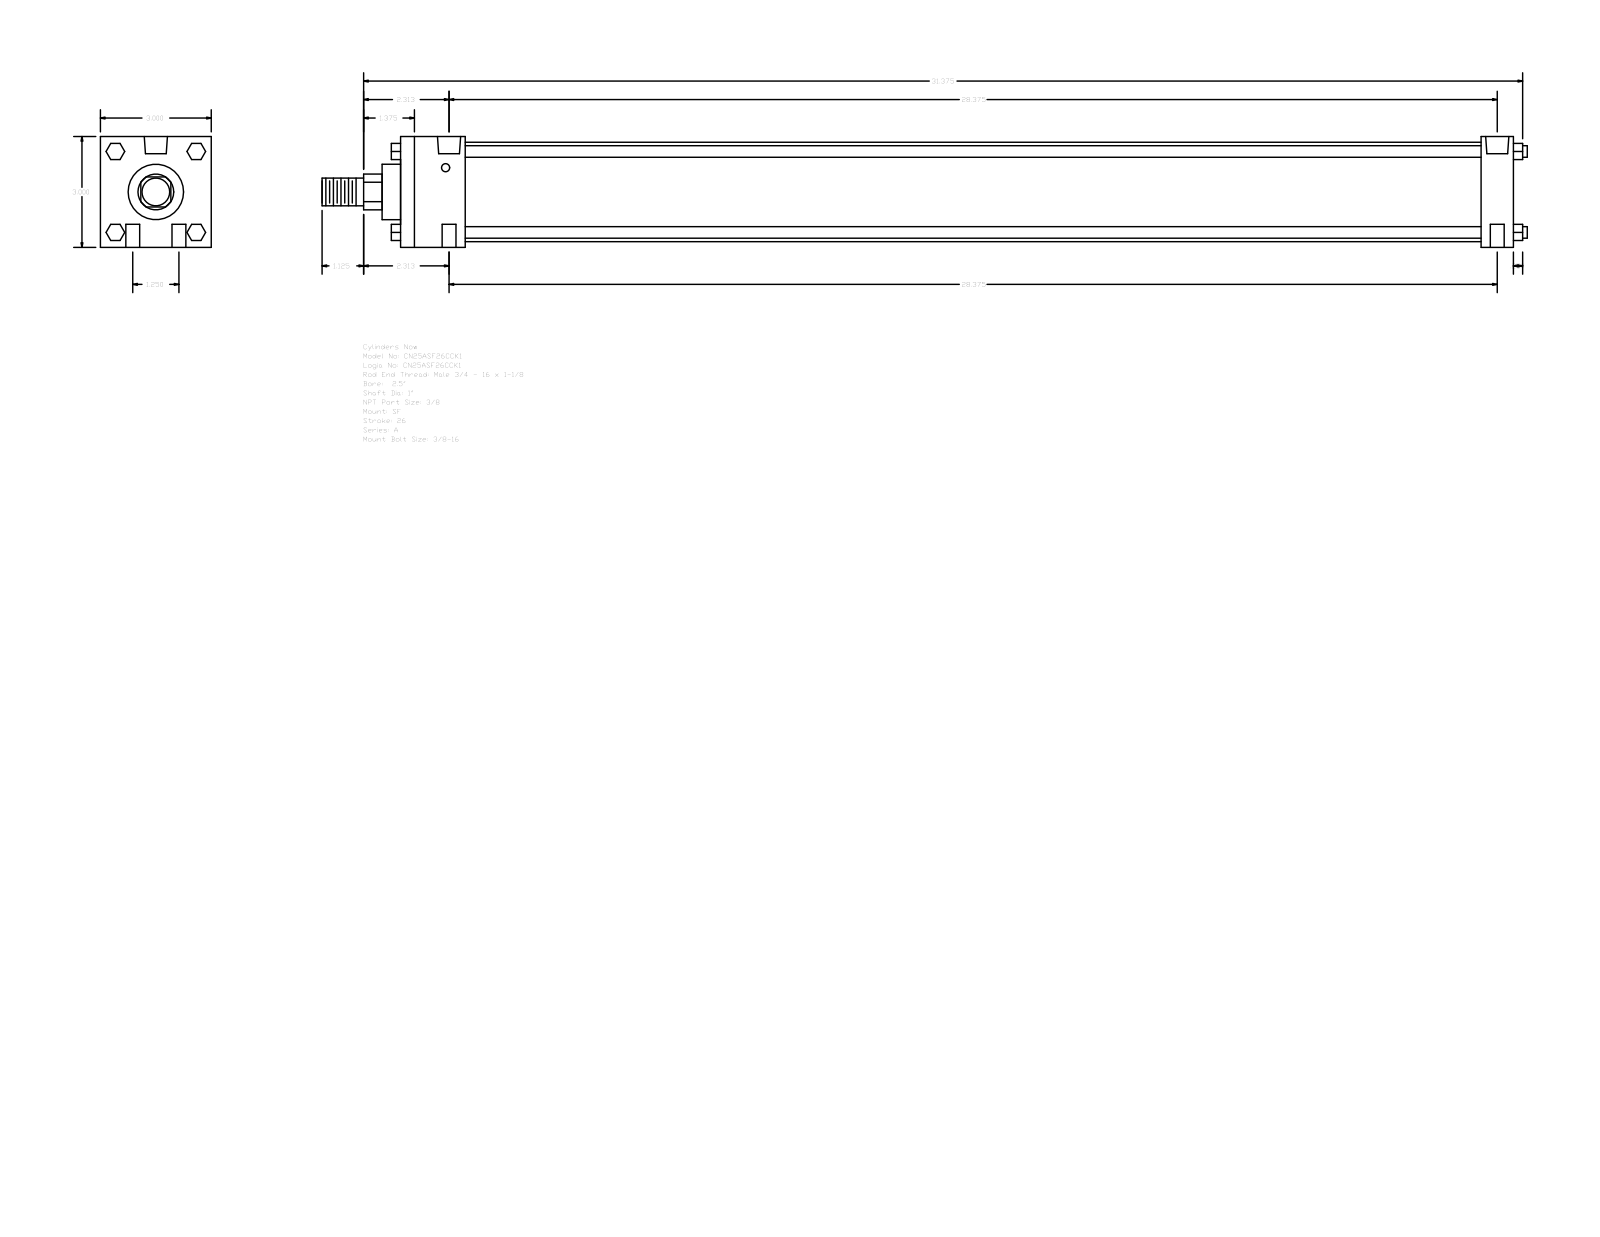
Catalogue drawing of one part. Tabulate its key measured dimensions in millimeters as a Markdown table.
| quantity | value |
| --- | --- |
| part name | A_SF__0250_1 |
| STEP written by | GSSL Pune (CONFIG_CONTROL_DESIGN) |
| units | millimeters |
| bodies | 0 solids, 124 faces (94 planar, 30 cylindrical, 0 other) |
| overall size | 828.67 × 76.2 × 76.2 |
| round holes (diameter × count) | 9.53 × 4, 5.56 × 2, 15.93 × 2 |
| round bosses / shafts (diameter × count) | 7.94 × 4, 68.33 × 1, 38.1 × 1, 25.4 × 1, 19.05 × 1 |
| partial cylindrical surfaces (radius × count) | 12.29 × 1 |
| main face-to-face distances | 76.2, 765.18, 742.95, 22.23, 44.45, 698.5, 720.73, 12.7, 11.11, 57.15 |
| hole center spacings | 15.88, 720.89, 720.72, 31.76, 721.42, 725.48 |
